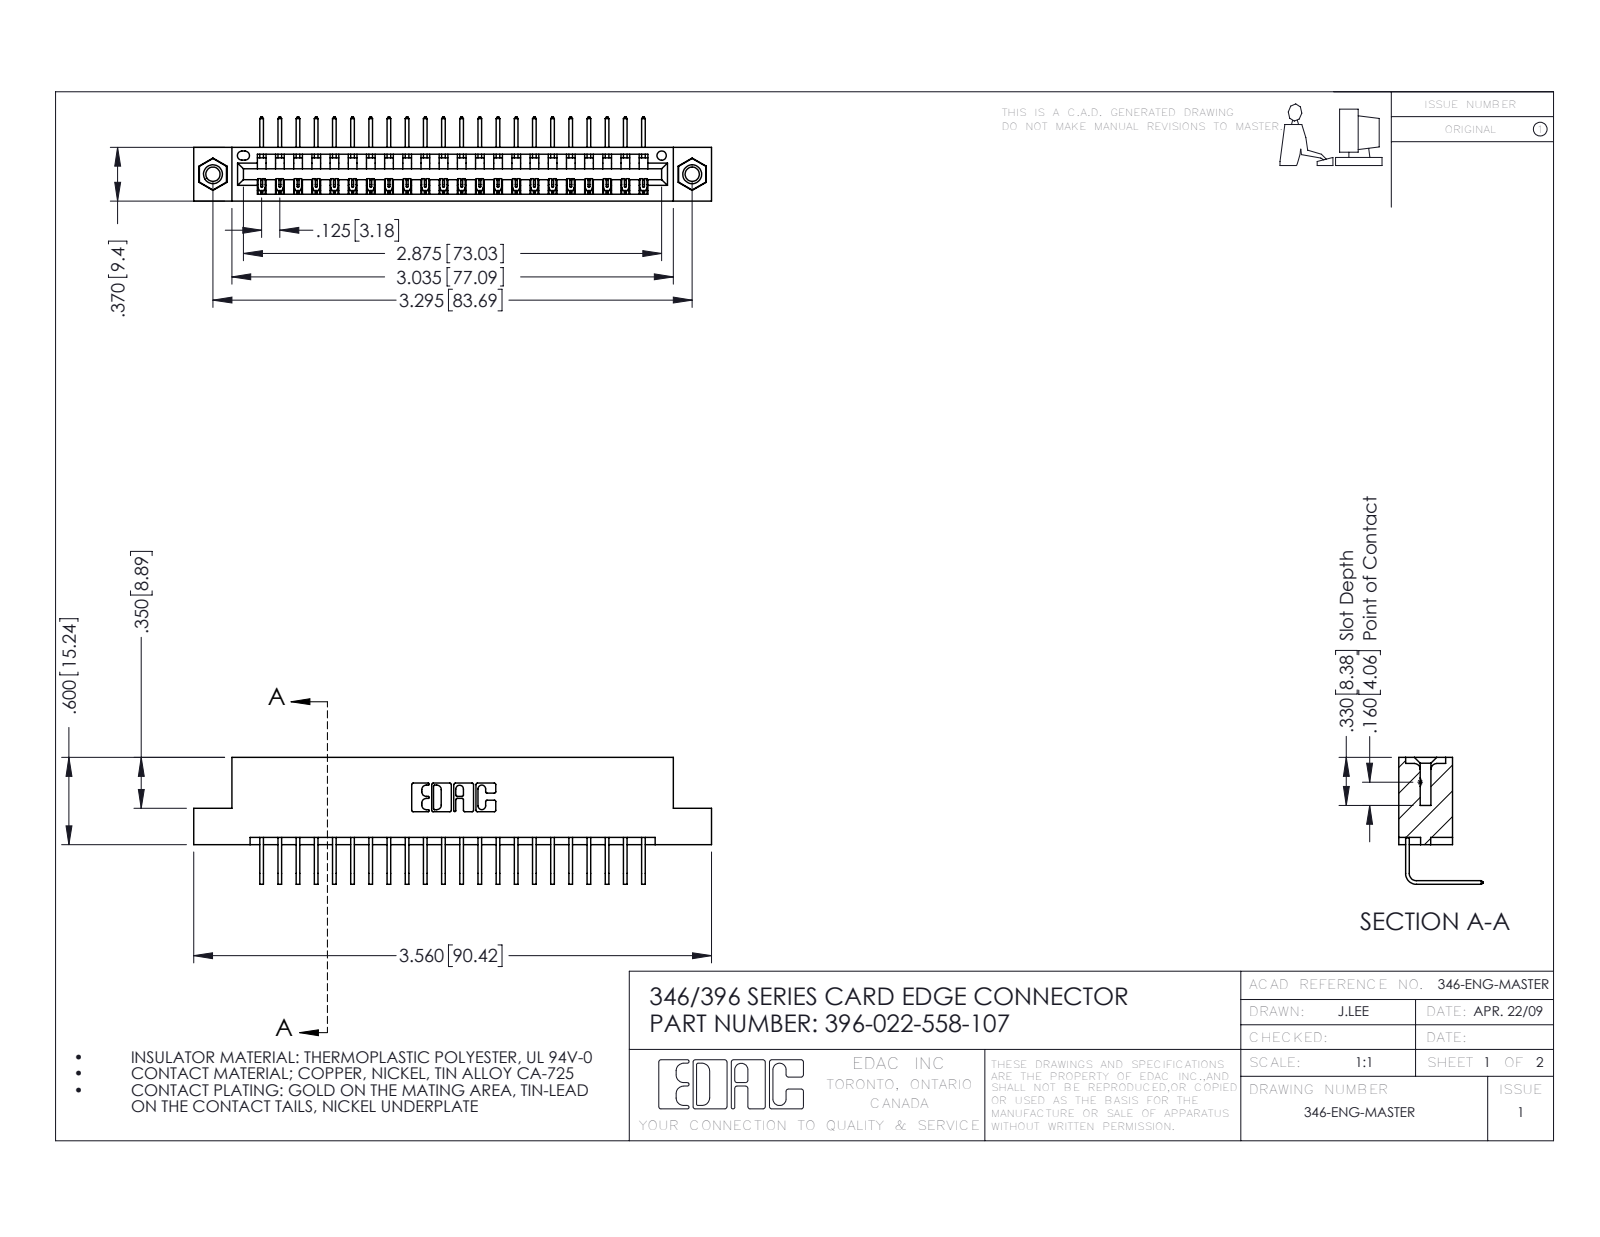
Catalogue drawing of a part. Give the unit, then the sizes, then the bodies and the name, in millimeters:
Units: millimetres
Overall size (bounding box): 90.4 × 22.2 × 14.7
Round holes (diameter × count): ⌀2.5 ×2, ⌀3.2 ×2, ⌀4 ×2, ⌀1.6 ×1
Round bosses / shafts (diameter × count): ⌀3.9 ×2
Partial cylindrical surfaces — rounded edges, fillets, slot ends (radius × count): R0.2 ×44, R0.3 ×22, R0.2 ×6, R0.8 ×6, R0.7 ×3, R0.8 ×2, R1 ×2, R0.4 ×1
Main face-to-face distances: 8.2, 1.2, 9.4, 6.4, 7.6, 0.6, 1.8, 3.8, 5.6, 2.5
Hole centre spacings: 6.2, 78.4, 83.7
Volume: 8 570 mm³ · Surface area: 10 970 mm²
Bodies: 25 solids, 1502 faces (1032 planar, 454 cylindrical, 16 other)
Part name (STEP PRODUCT): 346 Part_Flush Mounting Lugs - 0.156 Dia-TI; 345-250-001_345-250-005-103; 345-292-001_558 Tail - 2; 396-022-558-107
STEP written by: SolidWorks 2016 (CONFIG_CONTROL_DESIGN)
